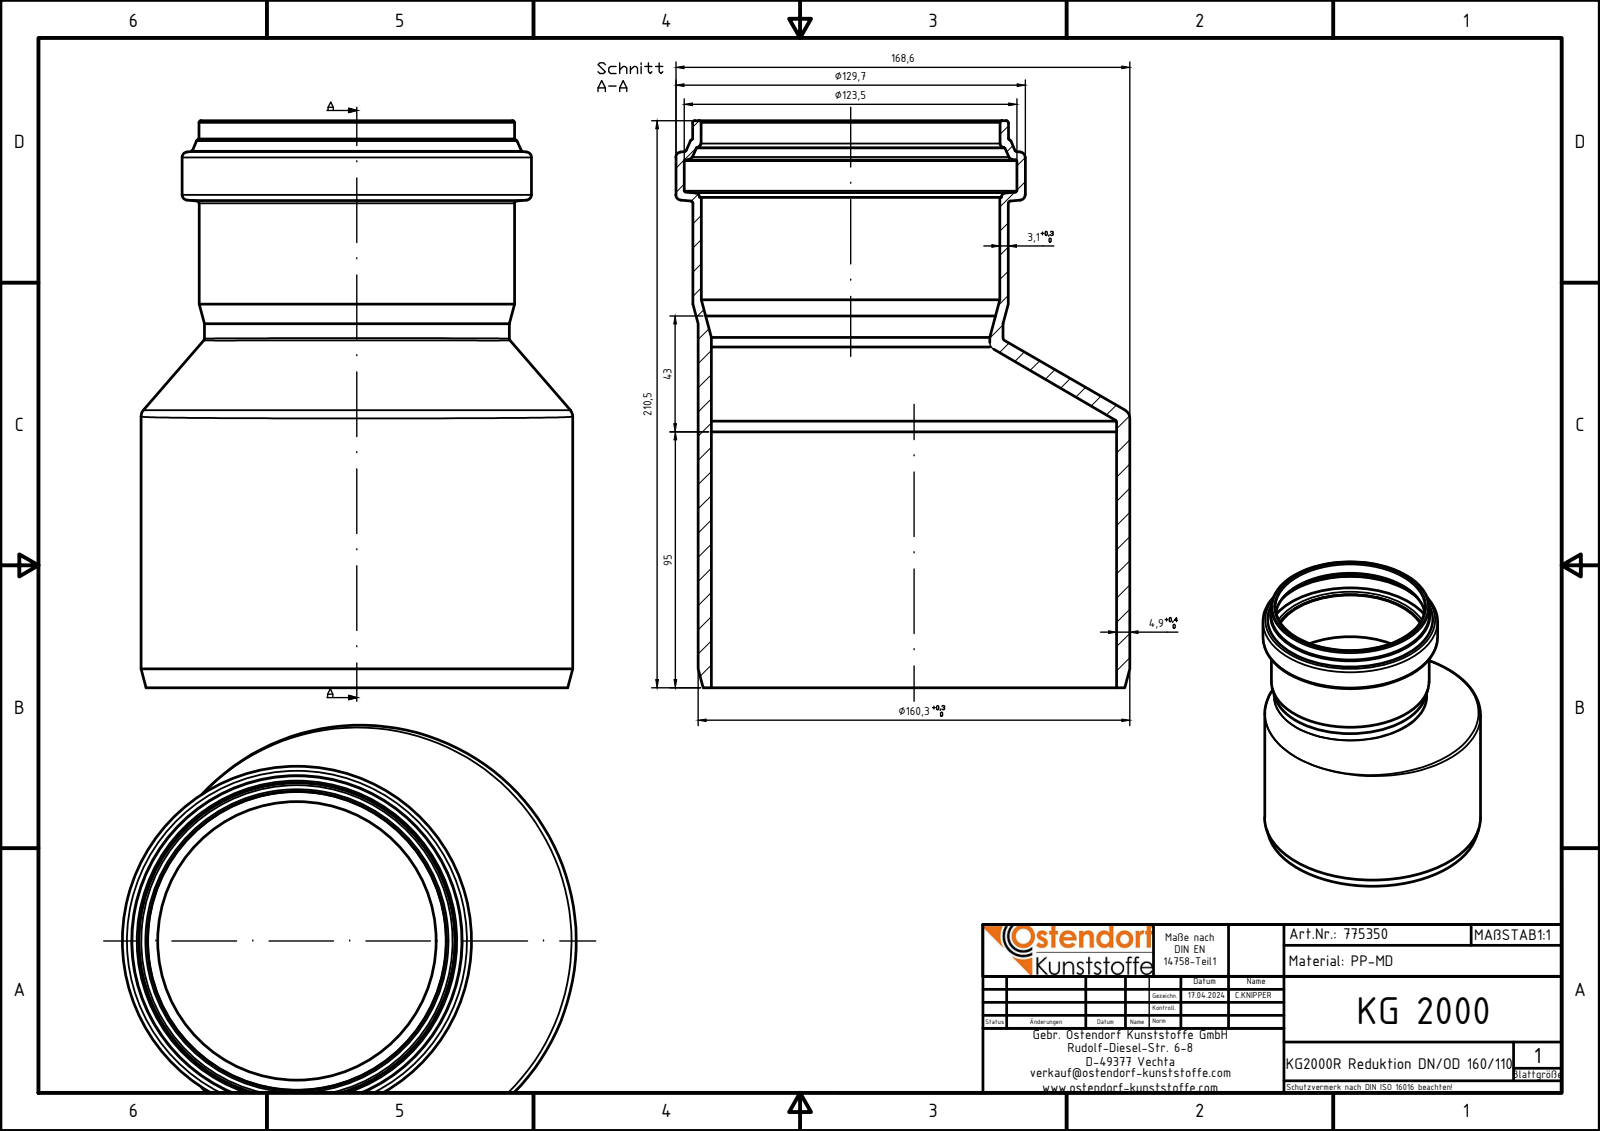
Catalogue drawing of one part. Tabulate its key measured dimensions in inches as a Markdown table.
| quantity | value |
| --- | --- |
| part name | 775350z |
| STEP written by | Autodesk Inventor 2024 (AUTOMOTIVE_DESIGN) |
| units | inches |
| bodies | 1 solid, 44 faces (3 planar, 11 cylindrical, 30 other) |
| overall size | 8.287 × 6.636 × 6.311 |
| volume | 26.16 in³ |
| surface area | 308.4 in² |
| round holes (diameter × count) | 4.071 × 1, 4.366 × 1, 4.37 × 1, 4.409 × 1, 4.862 × 1, 5.925 × 1 |
| round bosses / shafts (diameter × count) | 6.311 × 1, 5.106 × 1, 4.614 × 1, 4.61 × 1, 4.457 × 1 |
| main face-to-face distances | 8.287, 7.165, 1.122 |
| hole center spacings | 0.927 |
